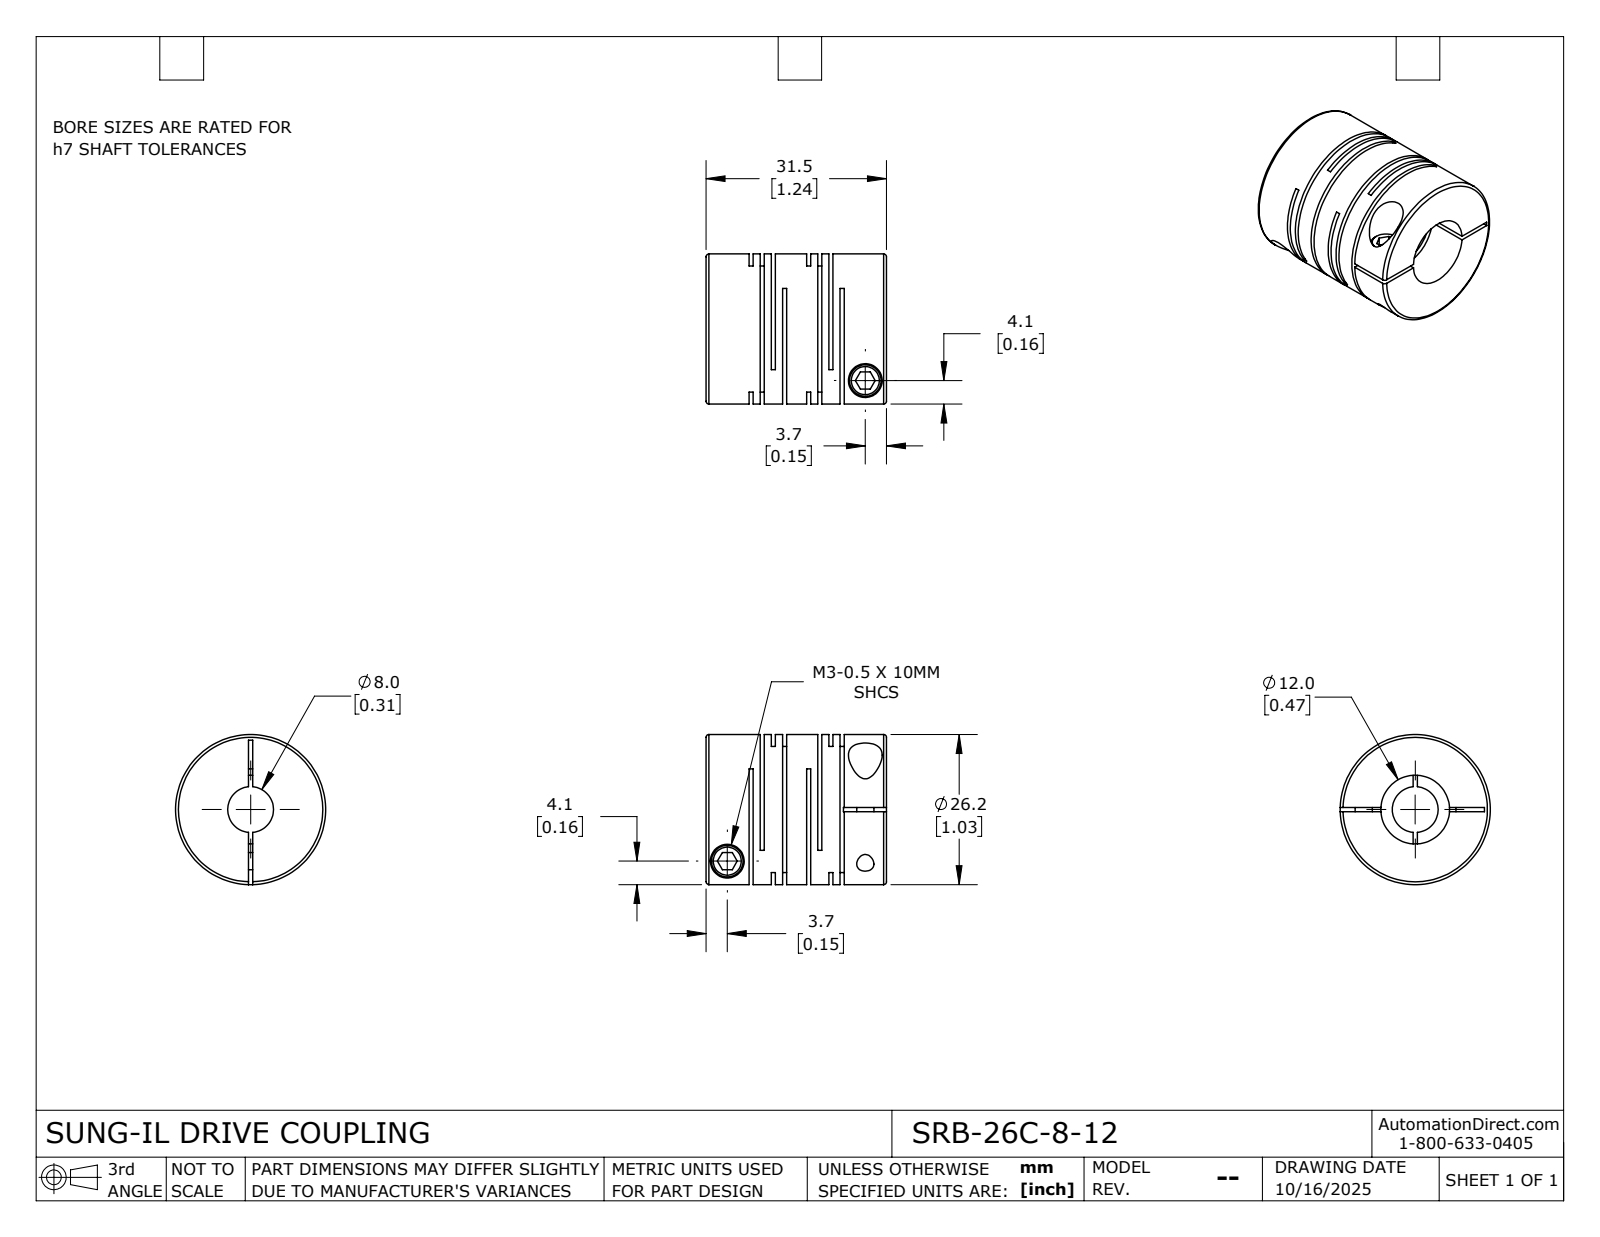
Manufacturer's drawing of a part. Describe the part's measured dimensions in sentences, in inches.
The part is named "SRB-26C-8-12". Its 3-D file was written by "SolidWorks 2024 (CONFIG_CONTROL_DESIGN)". It is 1 solid with 115 faces: 60 planar, 42 cylindrical and 13 other. Overall it measures 1.24 by 1.031 by 1.031 inches. Its volume is 0.703 cubic inches and its surface area 15.96 square inches. Round holes: 2 of diameter 0.118, 2 of diameter 0.232, 1 of diameter 0.315, 1 of diameter 0.472. Round bosses or shafts: 2 of diameter 0.217, 1 of diameter 1.031. The main face-to-face distances are 0.077, 0.396, 0.028, 0.154, 0.319, 0.472, 0.049, 0.105, 0.368, 0.549.
